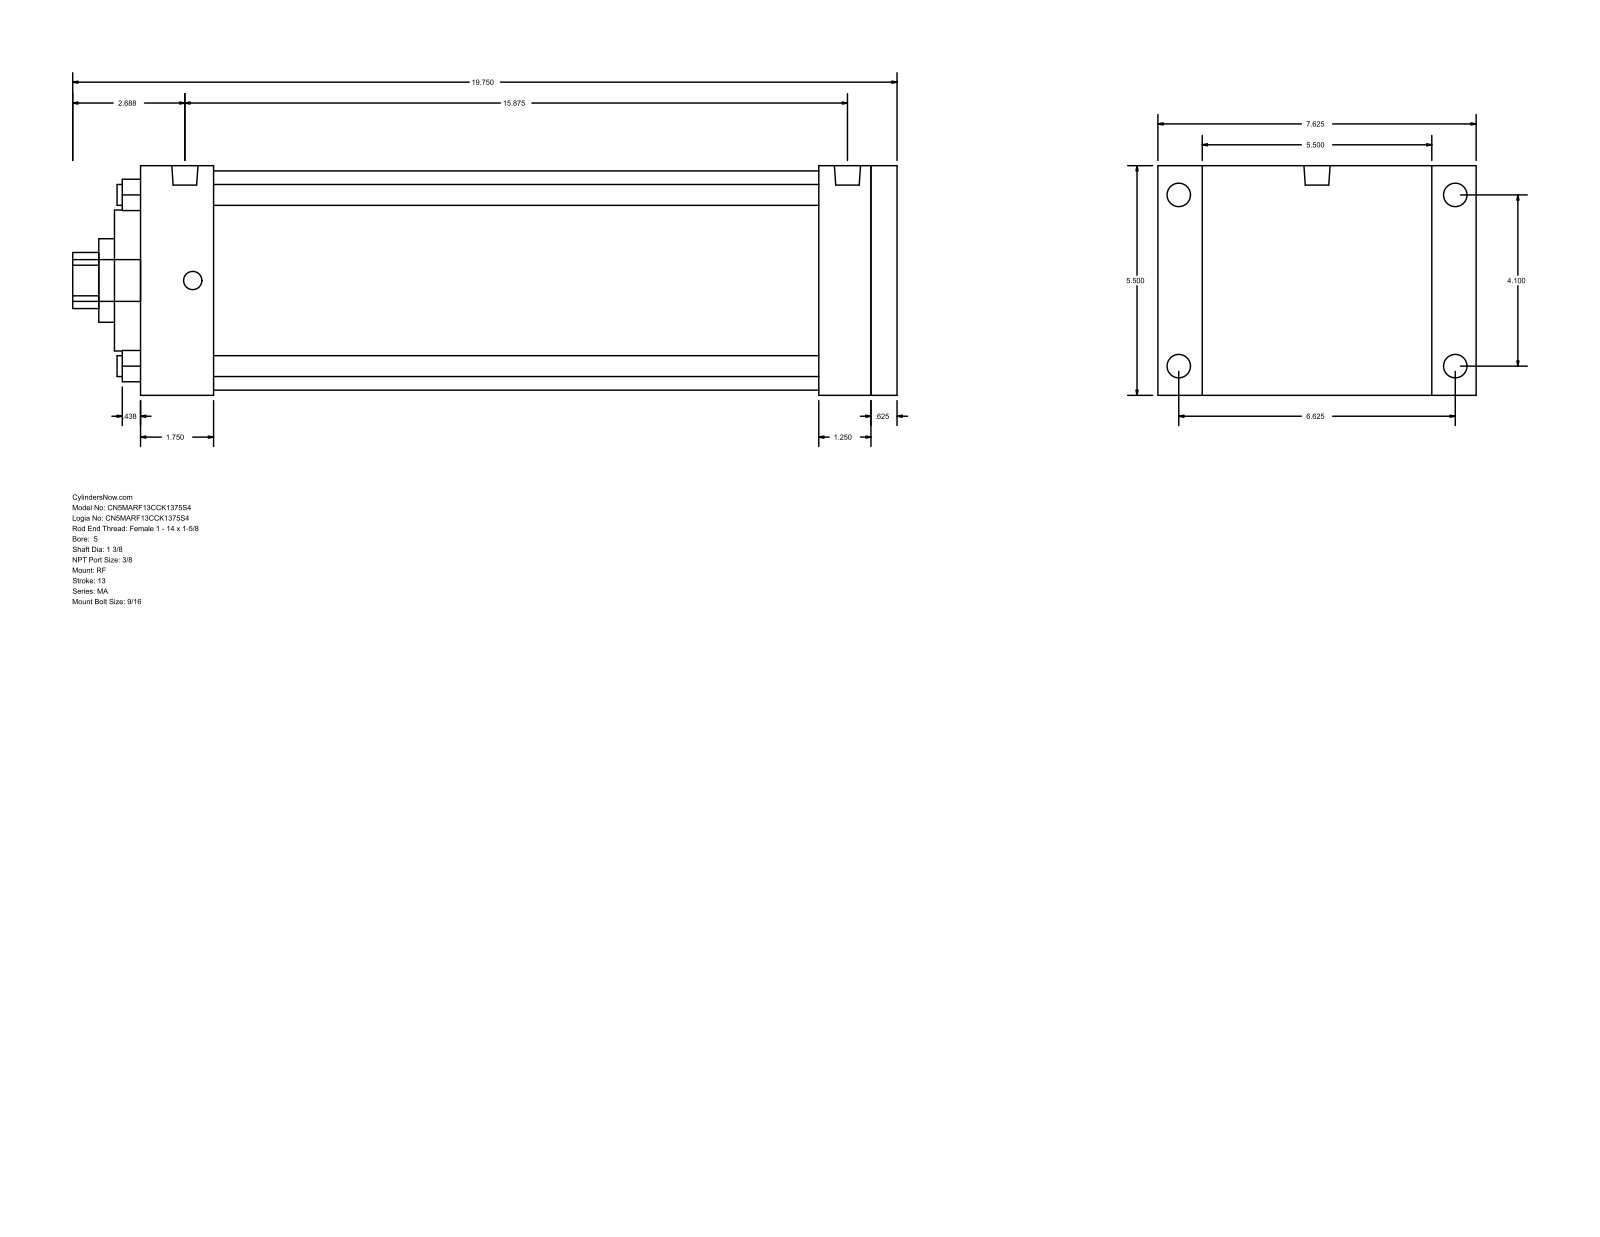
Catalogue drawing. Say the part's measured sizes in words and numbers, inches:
The part is named "MA_RF__0500_1.375". Its 3-D file was written by "GSSL Pune (CONFIG_CONTROL_DESIGN)". It is 0 solids with 94 faces: 65 planar, 29 cylindrical and 0 other. Overall it measures 19.75 by 7.625 by 5.5 inches. Round holes: 4 of diameter 0.5, 1 of diameter 1.375, 1 of diameter 2, 1 of diameter 3.375, 1 of diameter 5.25. Round bosses or shafts: 4 of diameter 0.563, 4 of diameter 0.437, 2 of diameter 0.627, 1 of diameter 1. Partial cylindrical surfaces (rounded edges, fillets, slot ends): 1 of radius 0.672. The main face-to-face distances are 5.5, 18.125, 0.625, 17.5, 1.75, 15.75, 16.375, 16.25, 14.5, 1.25. The hole center spacings are 2.899, 4.1, 5.798.
